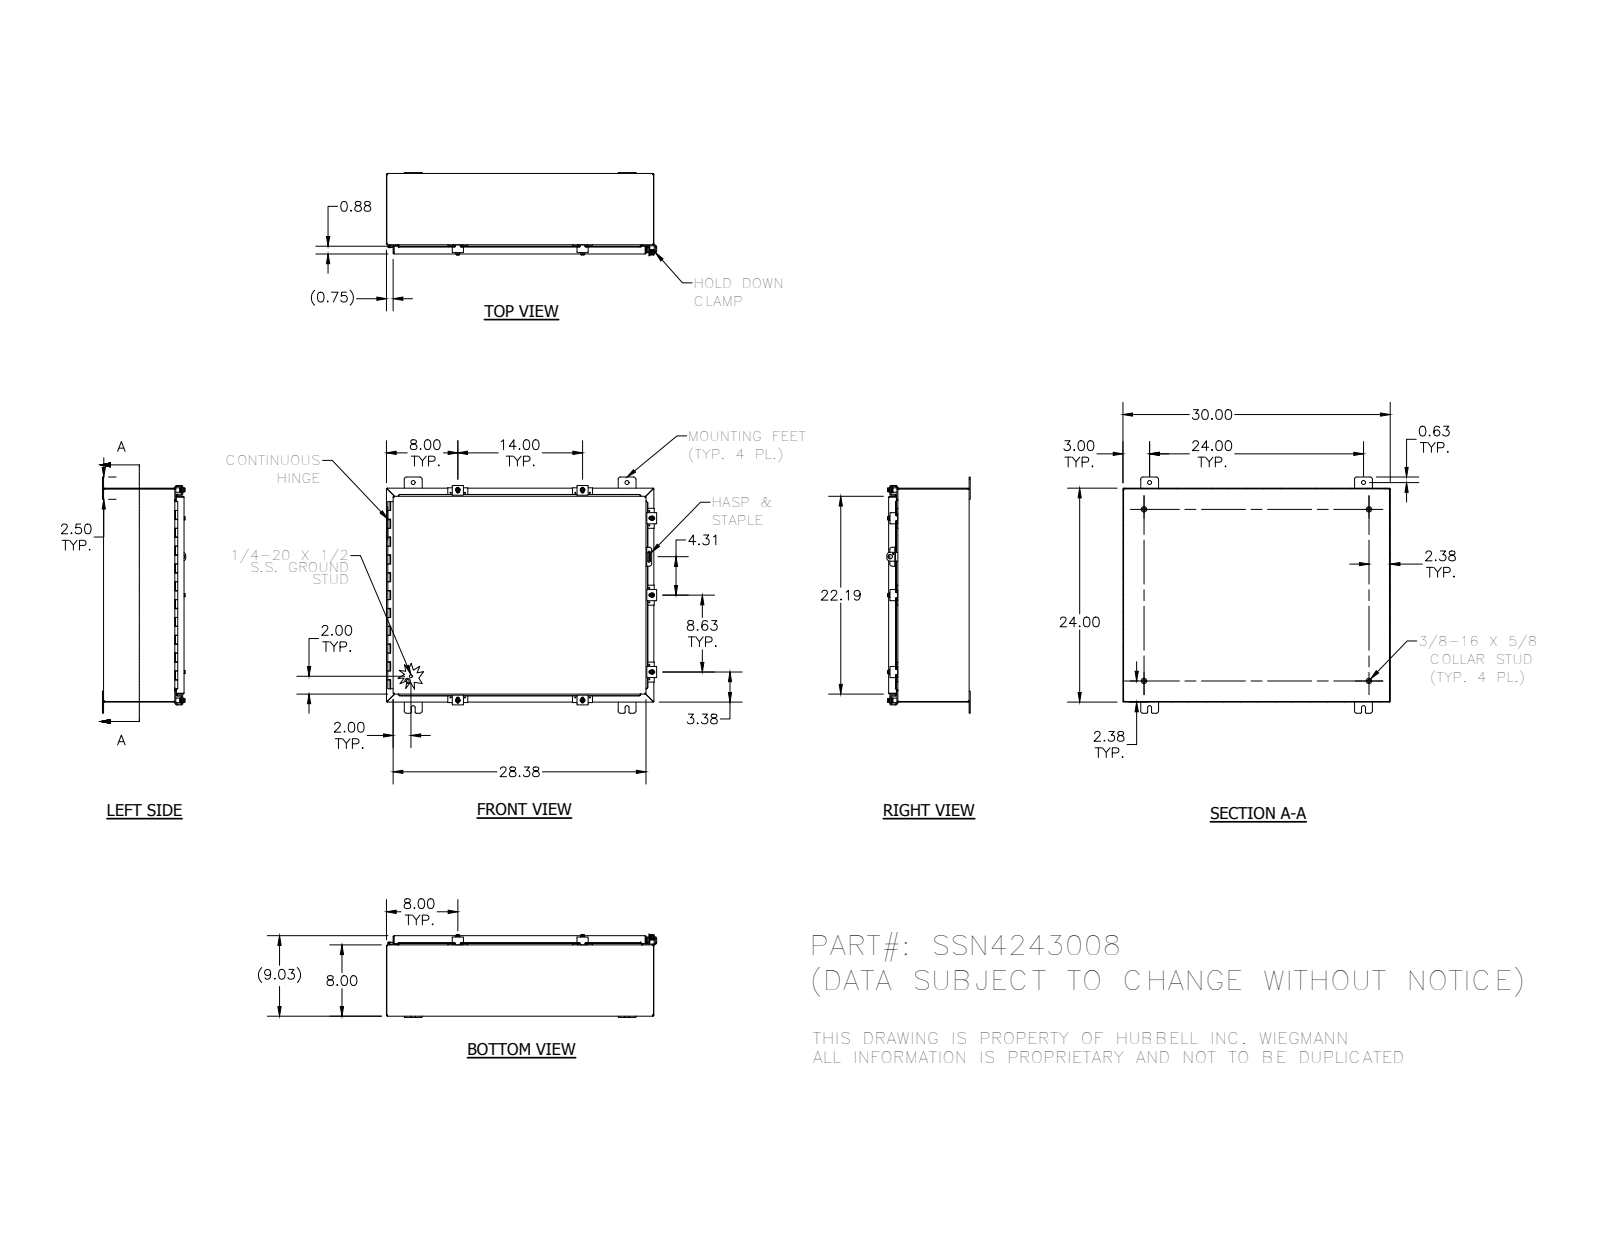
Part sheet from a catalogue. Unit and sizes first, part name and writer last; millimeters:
Units: millimetres
Overall size (bounding box): 769.9 × 673.1 × 237.6
Round holes (diameter × count): ⌀2.8 ×14, ⌀5.4 ×7, ⌀7.1 ×7, ⌀7.6 ×7, ⌀11.1 ×4, ⌀3.2 ×1, ⌀4 ×1, ⌀12.7 ×1
Round bosses / shafts (diameter × count): ⌀6.4 ×9, ⌀13.2 ×7, ⌀12.7 ×7, ⌀8.9 ×7, ⌀15.9 ×4, ⌀8.4 ×4, ⌀2.9 ×2, ⌀8.6 ×1
Partial cylindrical surfaces — rounded edges, fillets, slot ends (radius × count): R0.8 ×83, R3.2 ×37, R6.4 ×33, R0.8 ×23, R2.7 ×23, R1.6 ×15, R3.6 ×14, R2.5 ×10
Main face-to-face distances: 1.9, 227.6, 225.7, 229.4, 607.7, 760.1, 201.3, 26.2, 609.6, 605.8
Hole centre spacings: 22.3, 591.9, 355.6, 41.3, 335.1, 376.3, 583.2, 584.7
Volume: 3 395 000 mm³ · Surface area: 3 509 000 mm²
Bodies: 52 solids, 2042 faces (772 planar, 899 cylindrical, 371 other)
Part name (STEP PRODUCT): 30824; SSN42430LID; 328138T; 38859 (+8 more)
STEP written by: SolidWorks 2014 (AUTOMOTIVE_DESIGN)
